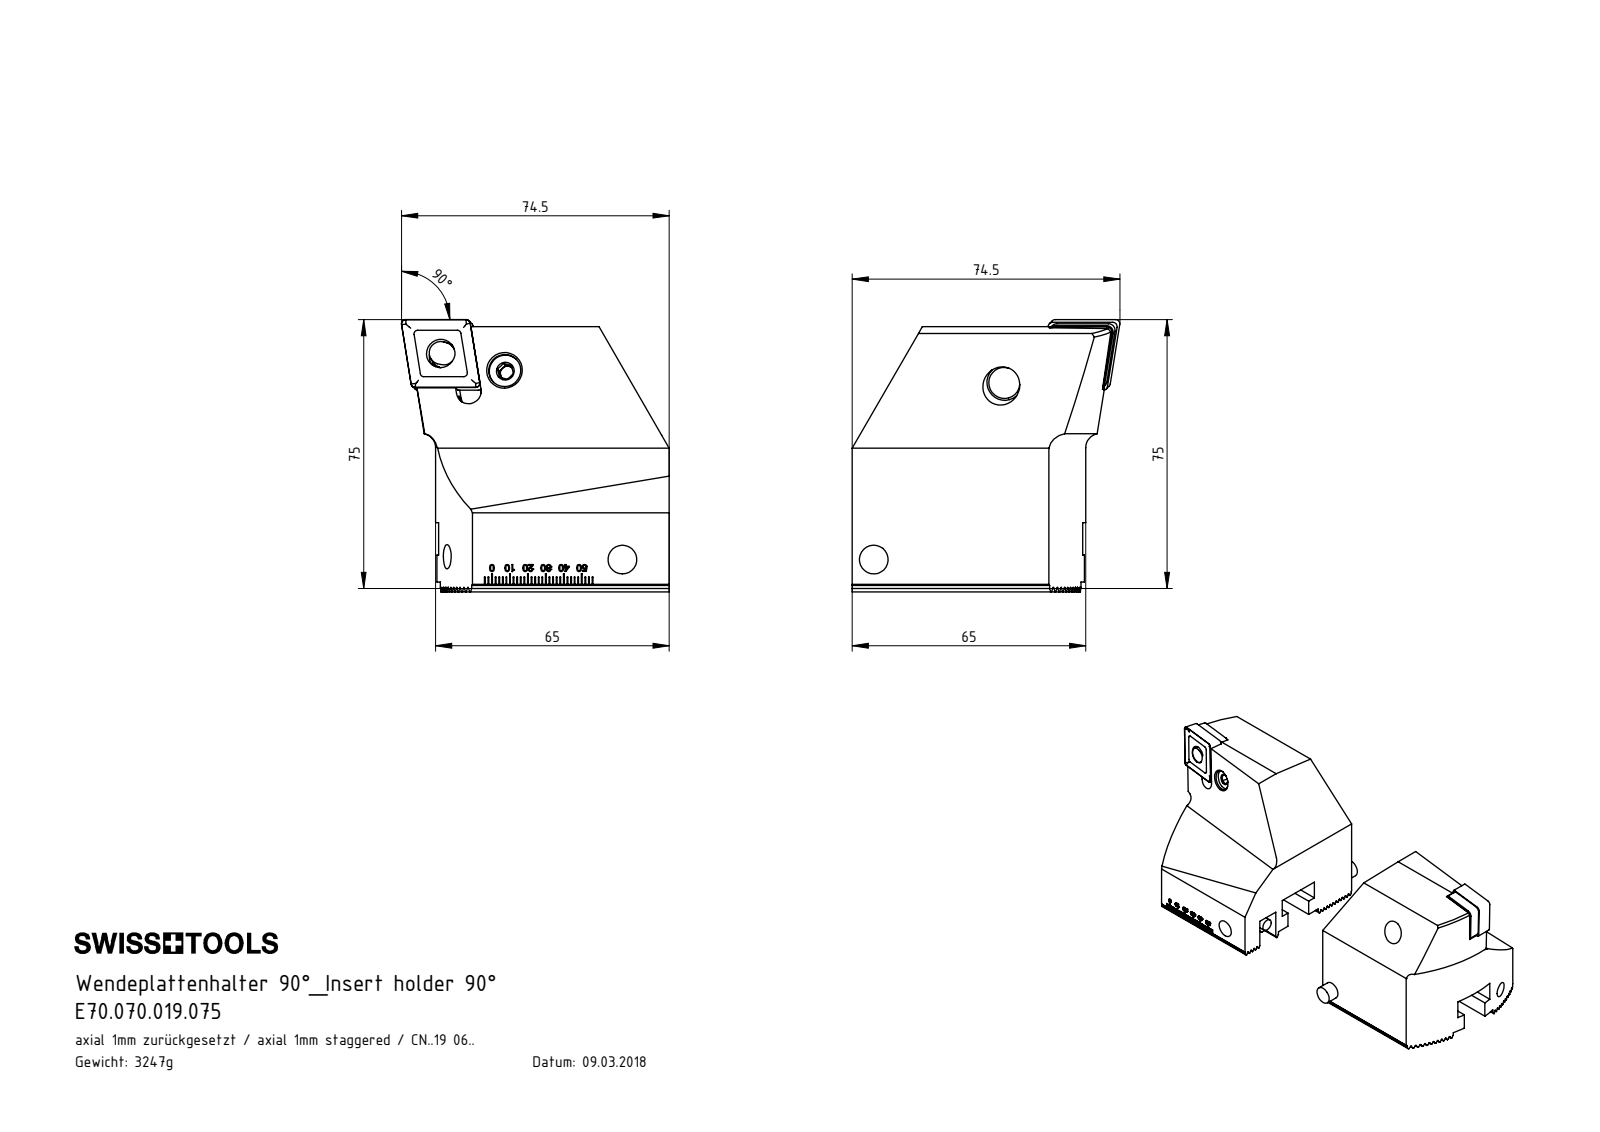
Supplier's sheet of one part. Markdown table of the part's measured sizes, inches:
| quantity | value |
| --- | --- |
| part name | WCF-ER3.101.000_A; WCF-ER1.101.000; E70.070.019.075; ISO 4028 - M8 x 35 (+6 more) |
| STEP written by | SolidWorks 2017 (CONFIG_CONTROL_DESIGN) |
| units | inches |
| bodies | 16 solids, 1300 faces (784 planar, 170 cylindrical, 346 other) |
| overall size | 7.876 × 3.304 × 2.984 |
| volume | 25.04 in³ |
| surface area | 113.8 in² |
| round holes (diameter × count) | 0.315 × 4, 0.268 × 2, 0.313 × 2, 0.354 × 2, 0.378 × 2, 0.402 × 2 |
| round bosses / shafts (diameter × count) | 0.394 × 2, 0.39 × 2, 0.339 × 2, 0.315 × 2, 0.217 × 2, 0.175 × 2 |
| partial cylindrical surfaces (radius × count) | 0.006 × 22, 0.047 × 8, 0.071 × 8, 0.163 × 8, 0.185 × 3, 0.122 × 2, 0.138 × 2, 0.144 × 2 |
| main face-to-face distances | 0.068, 0.273, 0.341, 2.756, 0.136, 0.205, 1.637, 1.705, 0.965, 1.791 |
| hole center spacings | 0.276, 0.729, 2.756, 0.012, 0.013, 0.74, 0.741, 1.575 |
